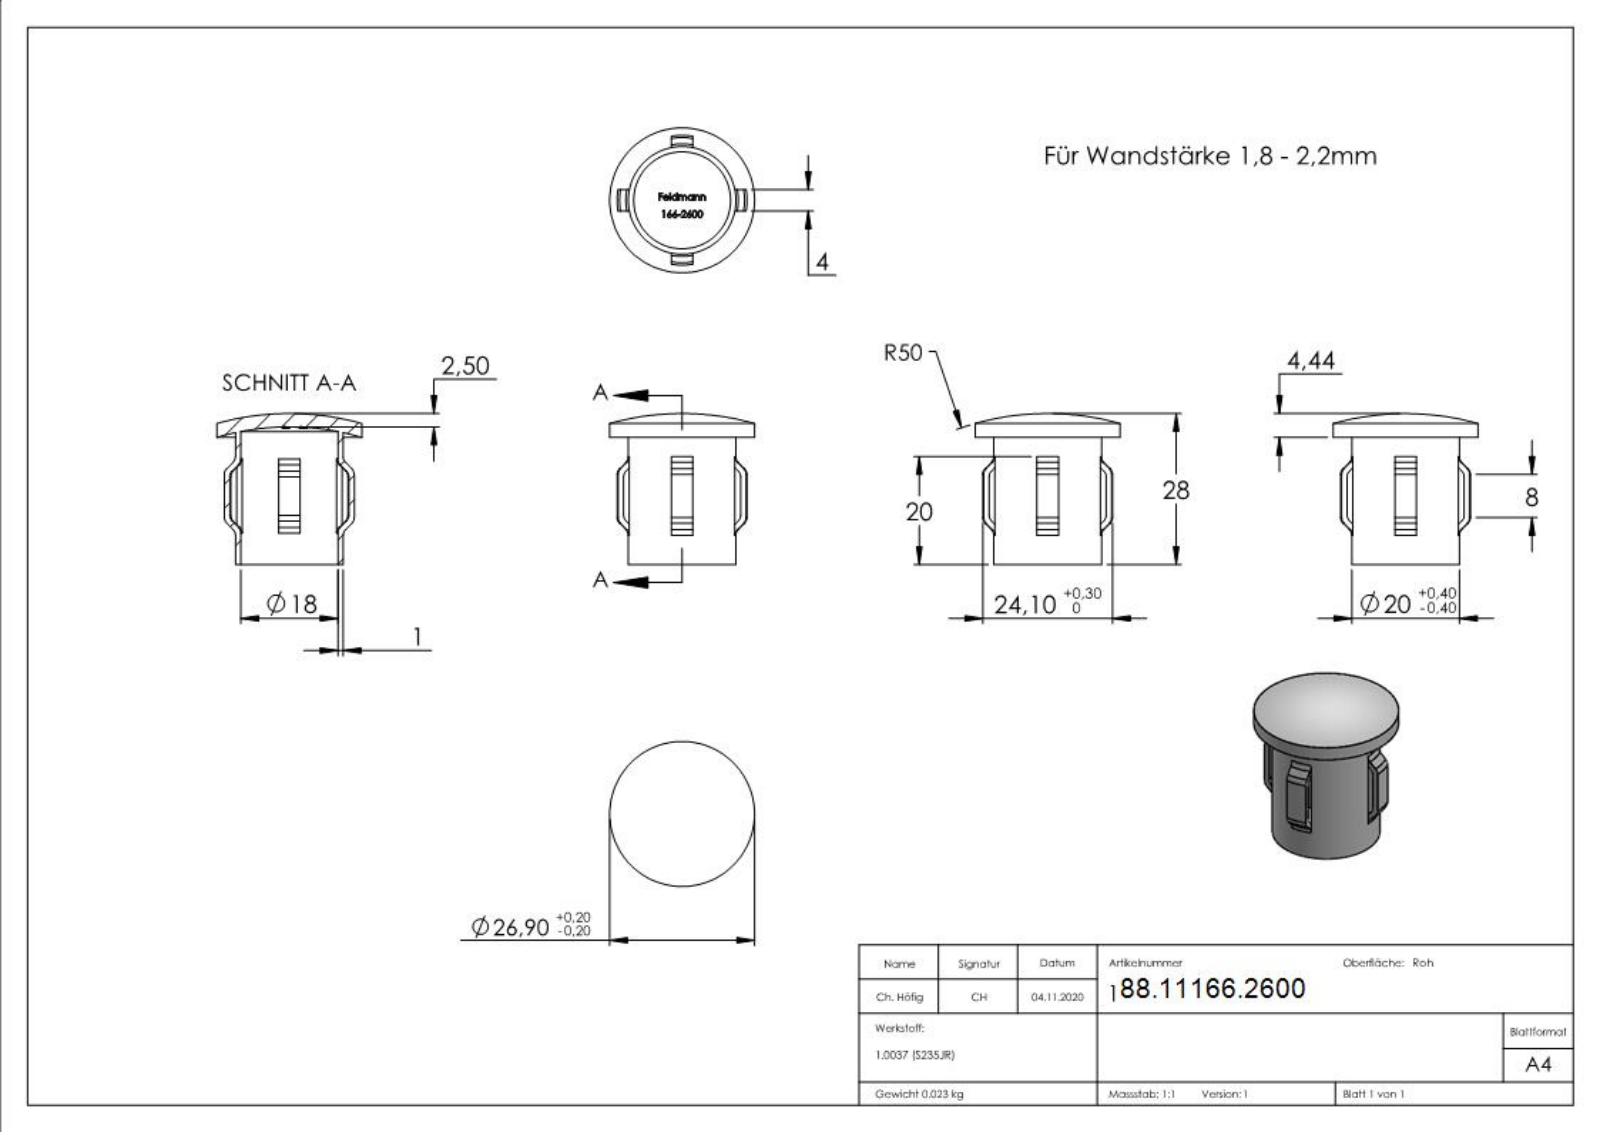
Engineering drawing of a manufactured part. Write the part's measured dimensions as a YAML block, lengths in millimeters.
part_name: "166-2600"
step_written_by: "SolidWorks 2018 (CONFIG_CONTROL_DESIGN)"
units: millimeters
bodies: {solids: 1, faces: 310, planar: 96, cylindrical: 16, other: 198}
overall_size: [28, 26.9, 26.9]
volume: 2940
surface_area: 4564
round_holes:
  - {diameter: 18, count: 1}
round_bosses_or_shafts:
  - {diameter: 26.9, count: 1}
  - {diameter: 20, count: 1}
partial_cylinders:
  - {radius: 11.05, count: 1}
  - {radius: 12.05, count: 1}
face_to_face_distances: [4, 2.97, 1.26, 2, 0.39, 3.66, 3.27, 0.87, 2.28, 0.99]
